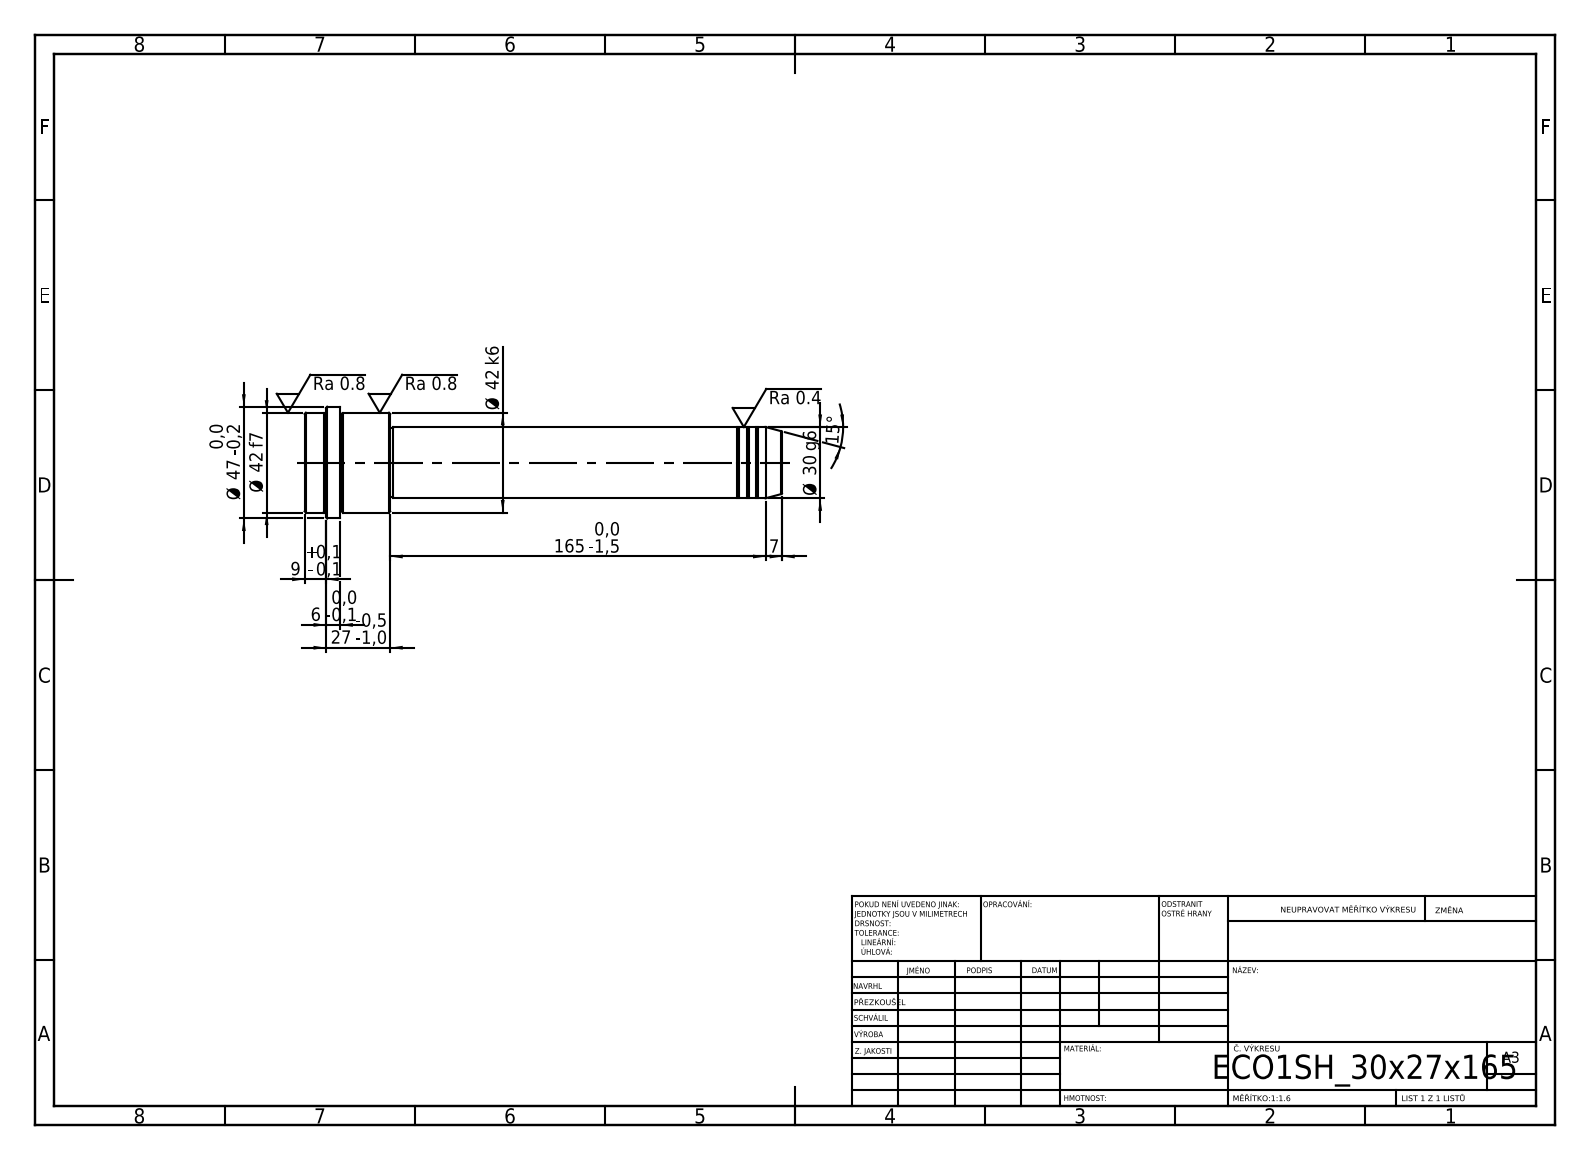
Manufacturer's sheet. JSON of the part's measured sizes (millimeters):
{"step_written_by": "SolidWorks 2019 (CONFIG_CONTROL_DESIGN)", "units": "millimeters", "bodies": {"solids": 1, "faces": 52, "planar": 6, "cylindrical": 16, "other": 30}, "overall_size": [201, 47, 47], "volume_mm3": 167700, "surface_area_mm2": 23935, "round_bosses_or_shafts": [[47, 1], [42, 1], [30, 1], [29, 1]], "face_to_face_distances": [36, 165, 201, 186, 21, 15, 192, 27, 6, 9]}
